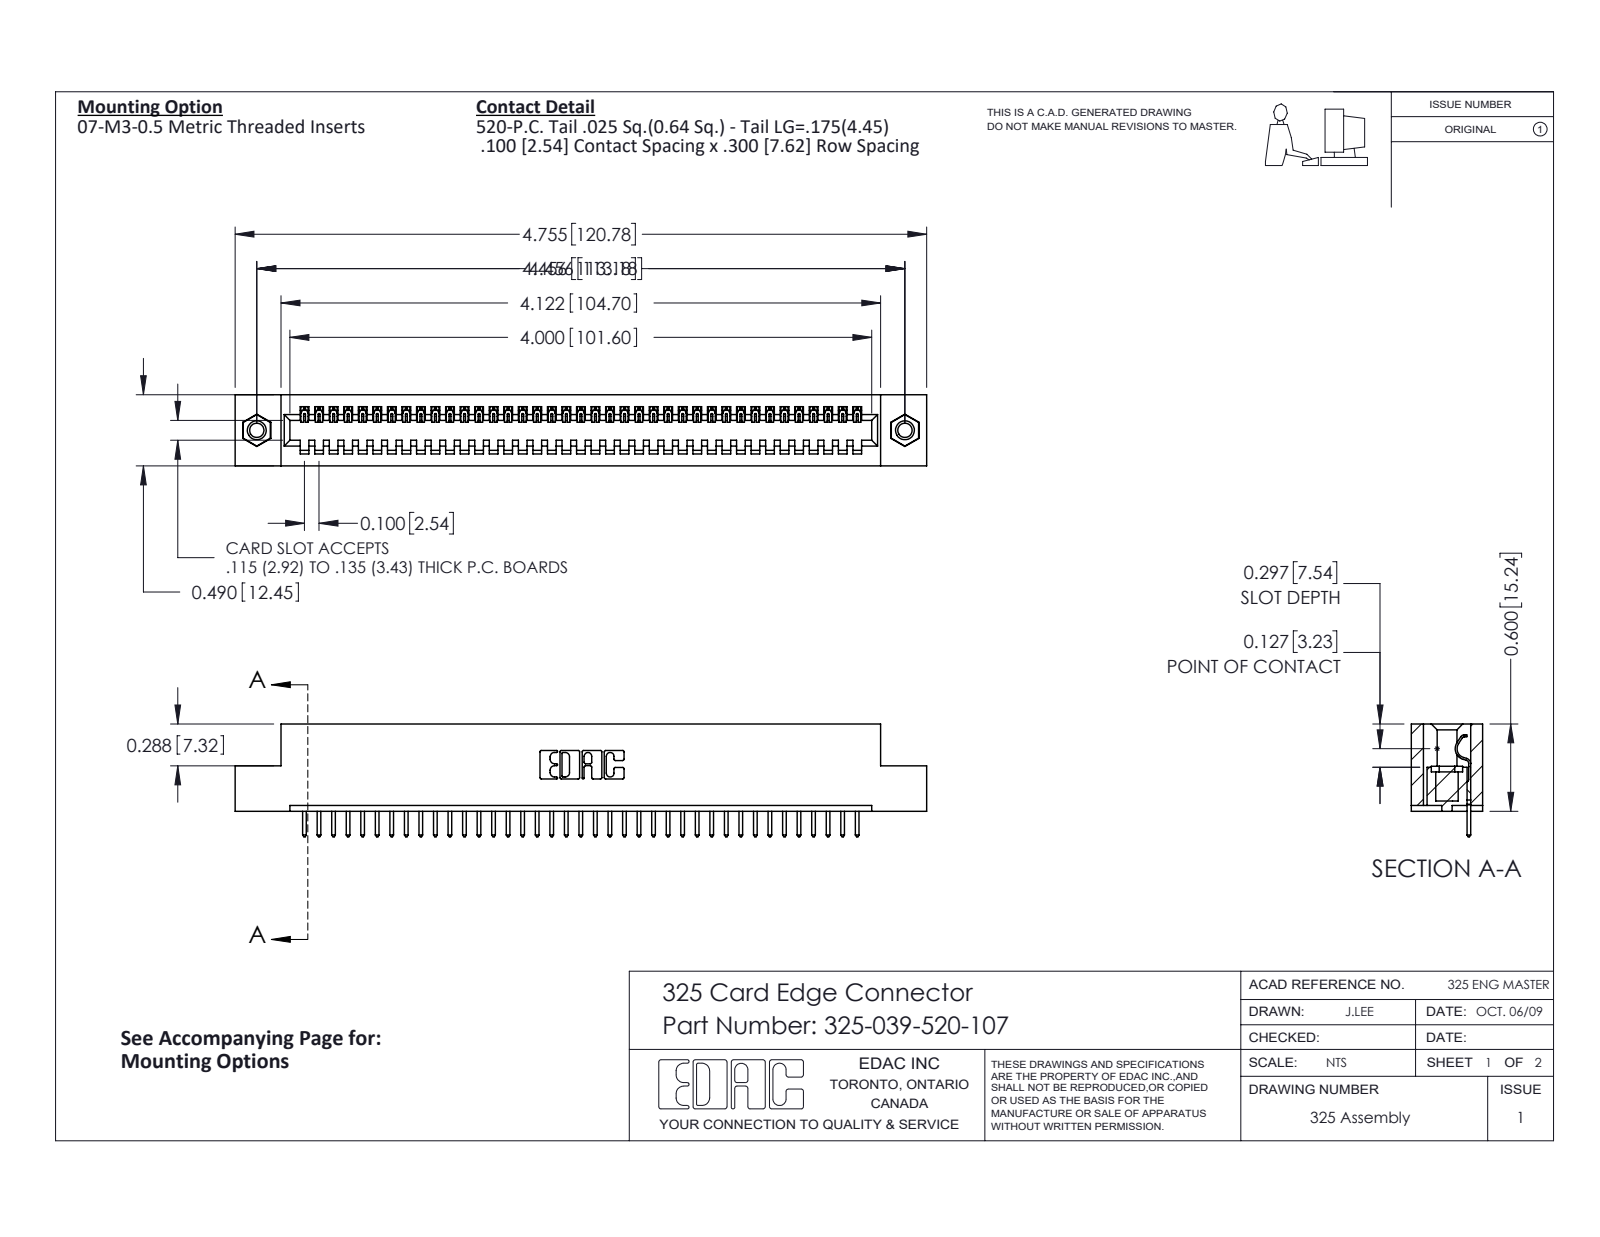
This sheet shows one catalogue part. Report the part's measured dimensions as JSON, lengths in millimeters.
{"part_name": "345-250-001_345-250-005-103; 325-292-001_325-293-120; 325 Part_TI; 325-039-520-107", "step_written_by": "SolidWorks 2016 (CONFIG_CONTROL_DESIGN)", "units": "millimeters", "bodies": {"solids": 42, "faces": 2436, "planar": 1740, "cylindrical": 680, "other": 16}, "overall_size": [120.8, 19.7, 12.4], "volume_mm3": 15200, "surface_area_mm2": 16170, "round_holes": [[2.5, 2], [3.2, 2], [4.1, 2]], "round_bosses_or_shafts": [[3.9, 2]], "partial_cylinders_radius": [[0.2, 78], [0.3, 78], [0.3, 22], [0.2, 6], [0.8, 6], [0.7, 3], [0.4, 1], [0.6, 1]], "face_to_face_distances": [2.1, 10.3, 12.4, 7.6, 2.7, 9.7, 0.6, 8.3, 14.2, 1], "hole_center_spacings": [113.2]}
